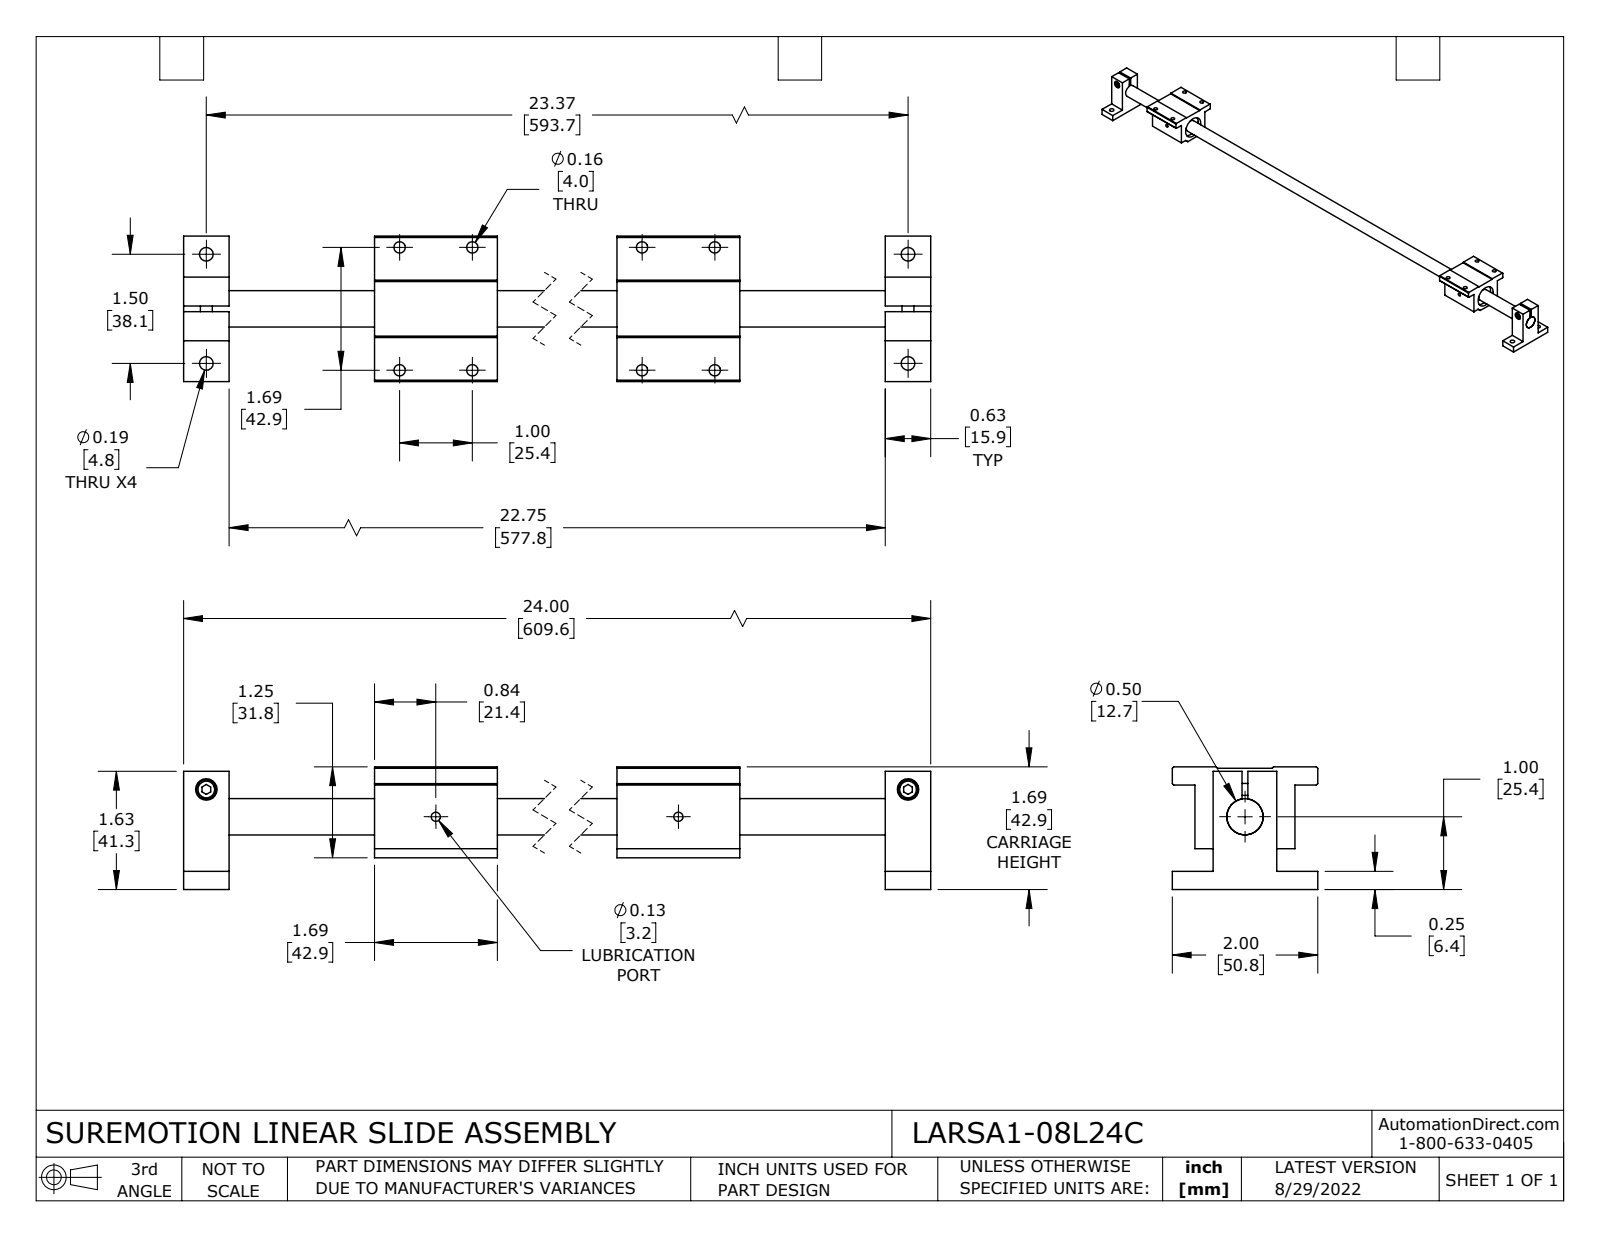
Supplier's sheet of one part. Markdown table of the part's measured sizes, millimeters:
| quantity | value |
| --- | --- |
| part name | LARSA1-08L24C_RAIL; LARSA1-08L24C; LARSACC-001 |
| STEP written by | SolidWorks 2021 (CONFIG_CONTROL_DESIGN) |
| units | millimeters |
| bodies | 7 solids, 160 faces (96 planar, 60 cylindrical, 4 other) |
| overall size | 609.6 × 50.8 × 42.8 |
| volume | 189 900 mm³ |
| surface area | 59 140 mm² |
| round holes (diameter × count) | 4 × 8, 4.8 × 4, 3.2 × 2, 7.5 × 2, 12.7 × 1, 22.2 × 1 |
| round bosses / shafts (diameter × count) | 6.9 × 2, 4.2 × 2 |
| main face-to-face distances | 6.4, 28.6, 34.9, 50.8, 22.2, 433.3, 36.5, 593.7, 15.9, 0.5 |
| hole center spacings | 433.3, 25.4, 42.9, 49.8, 67.5, 78.7, 92.9, 101.3 |
